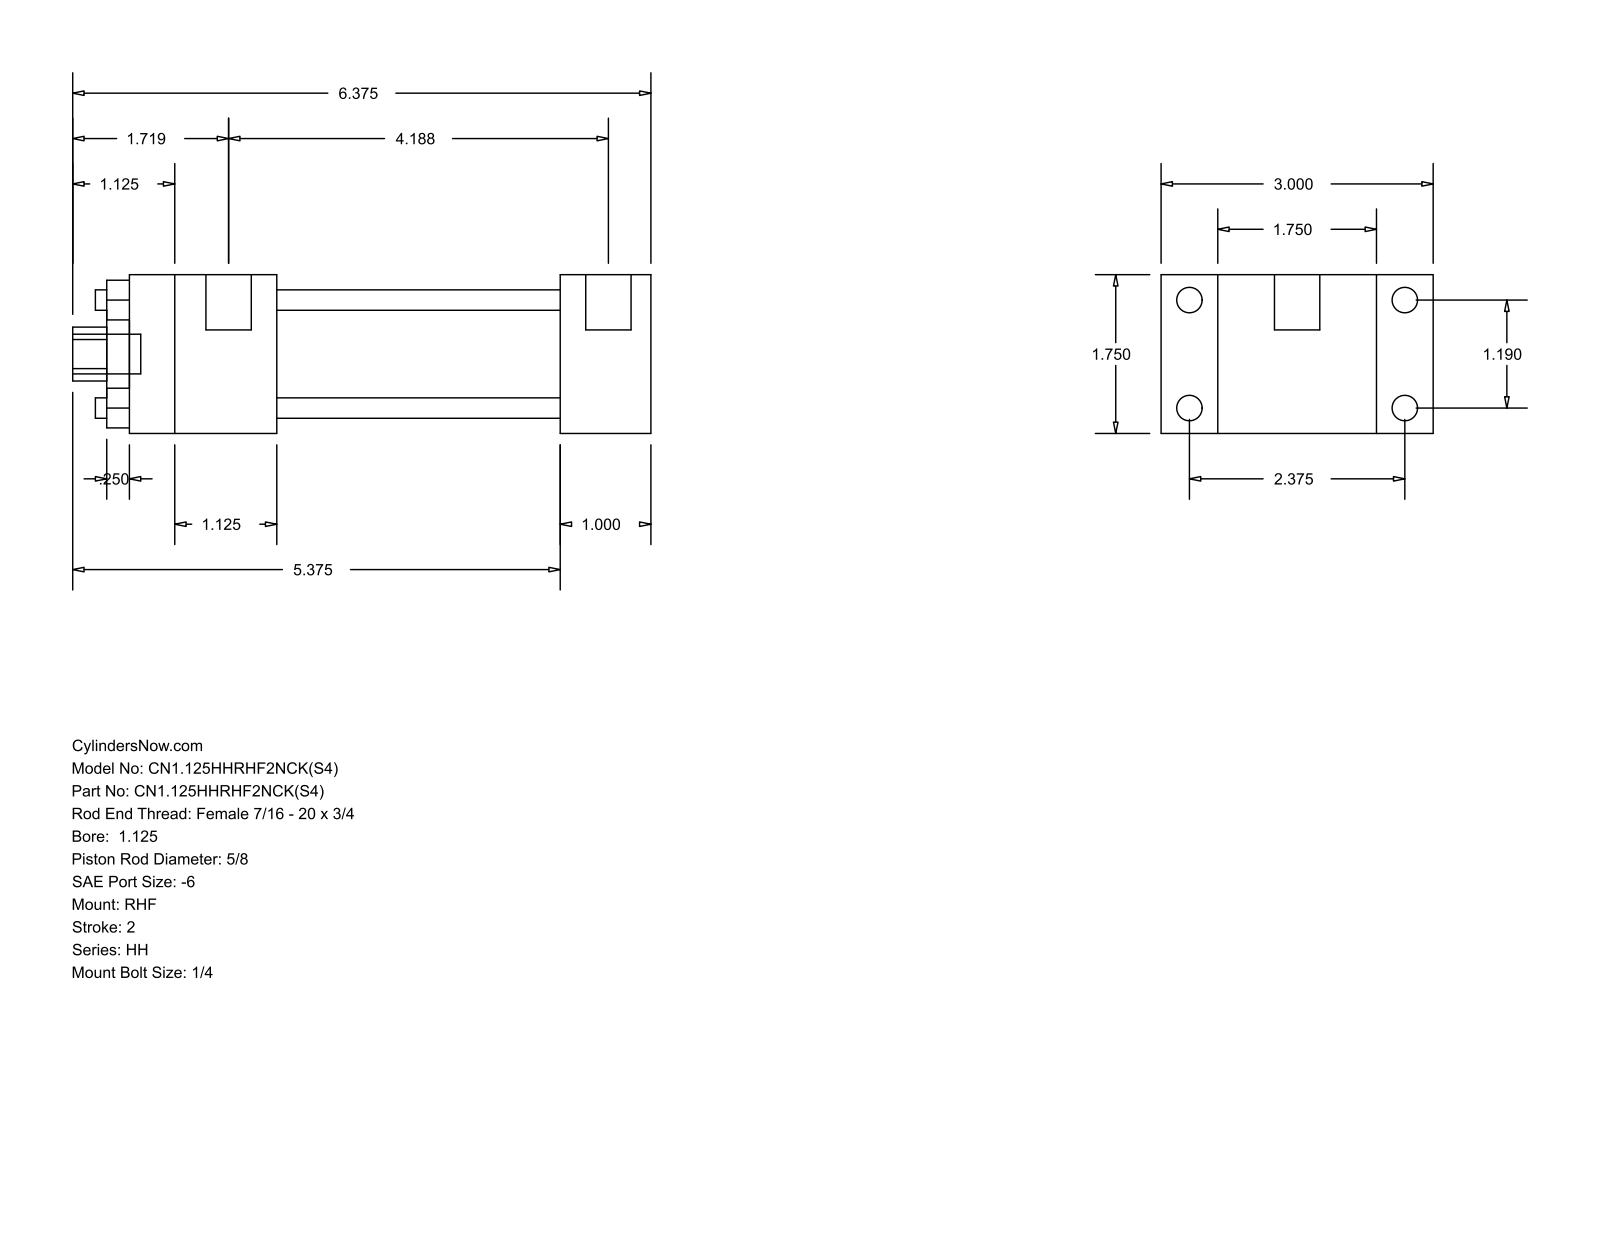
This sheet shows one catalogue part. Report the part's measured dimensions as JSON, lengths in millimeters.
{"part_name": "HH_RHF__0112_0.625", "step_written_by": "GSSL Pune (CONFIG_CONTROL_DESIGN)", "units": "millimeters", "bodies": {"solids": 0, "faces": 88, "planar": 60, "cylindrical": 28, "other": 0}, "overall_size": [161.93, 76.2, 44.45], "round_holes": [[5.71, 4], [15.88, 1], [28.57, 1], [34.92, 1]], "round_bosses_or_shafts": [[7.14, 4], [5.56, 4], [12.7, 2], [11.11, 1]], "partial_cylinders_radius": [[7.54, 1]], "face_to_face_distances": [44.46, 15.87, 60.33, 25.4, 76.2, 79.38, 104.78, 41.27, 120.65, 146.05], "hole_center_spacings": [21.37, 30.22, 42.74]}
